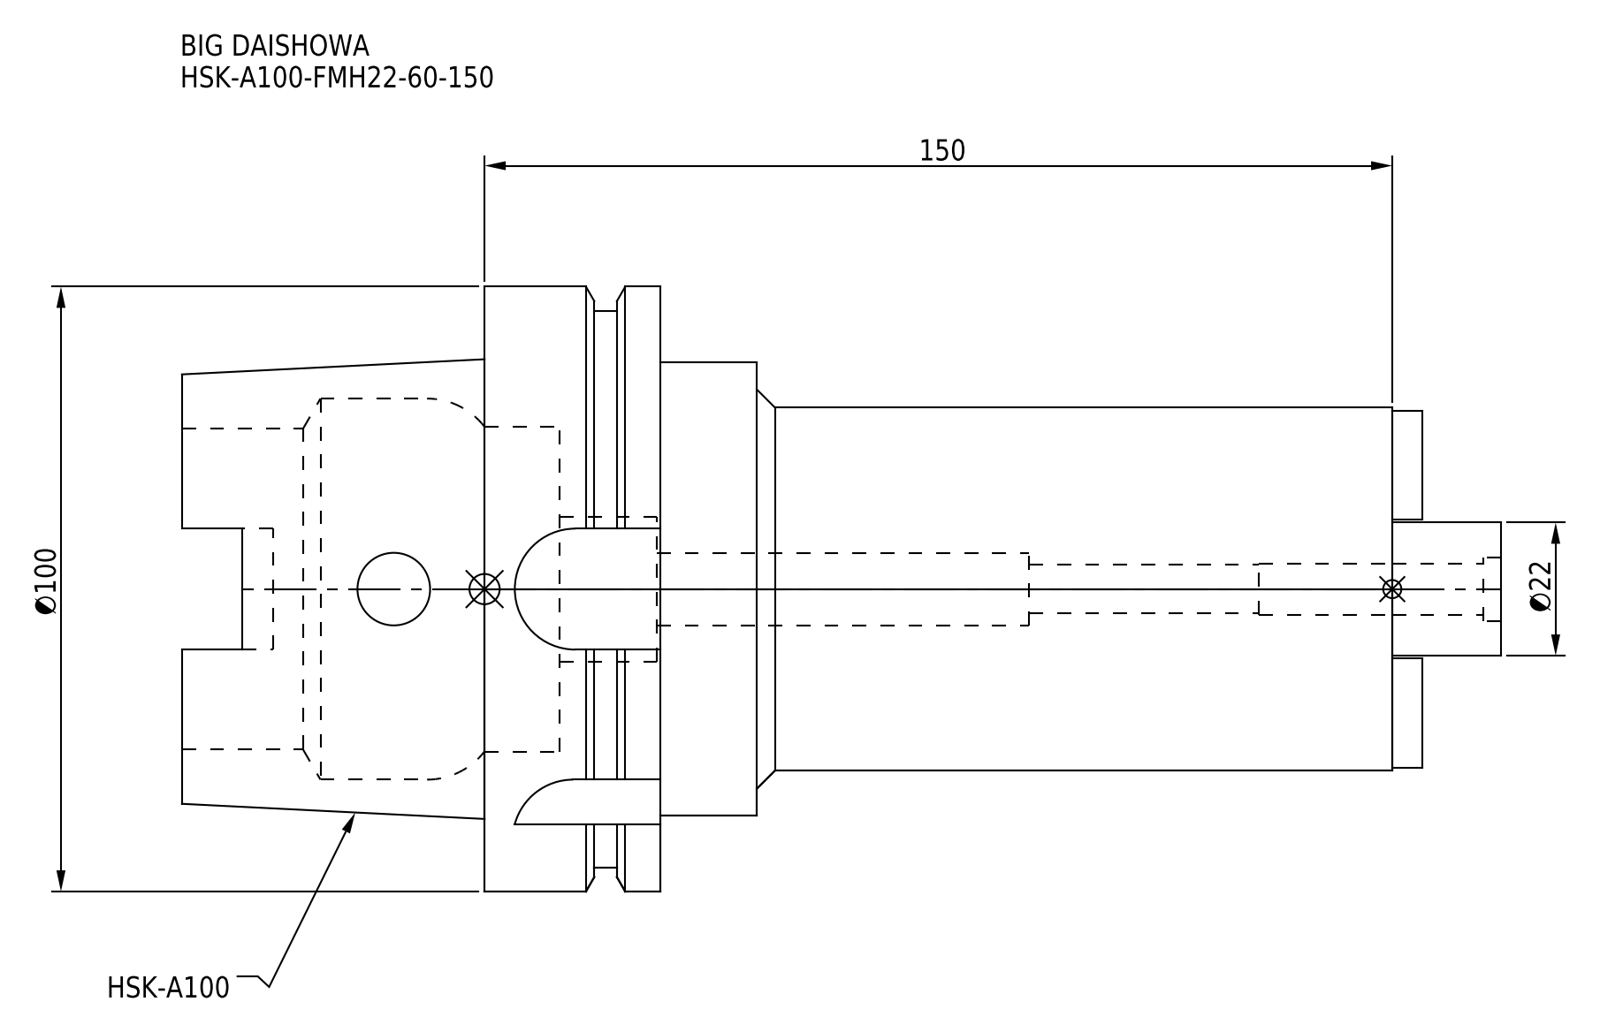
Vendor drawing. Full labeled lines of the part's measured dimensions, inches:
Part name (STEP PRODUCT): HSK-A100-FMH22-60-150
STEP written by: CREO PARAMETRIC BY PTC INC, 2016380 (AUTOMOTIVE_DESIGN)
Units: inches
Bodies: 1 solid, 109 faces (47 planar, 46 cylindrical, 16 other)
Overall size (bounding box): 8.583 × 3.937 × 3.937
Volume: 37.8 in³ · Surface area: 122.9 in²
Round holes (diameter × count): ⌀0.472 ×2, ⌀0.315 ×1, ⌀0.335 ×1, ⌀0.413 ×1, ⌀0.945 ×1, ⌀2.087 ×1, ⌀2.118 ×1, ⌀2.48 ×1
Round bosses / shafts (diameter × count): ⌀3.937 ×1, ⌀3.622 ×1, ⌀2.953 ×1, ⌀2.362 ×1, ⌀0.866 ×1
Partial cylindrical surfaces — rounded edges, fillets, slot ends (radius × count): R0.192 ×4, R0.394 ×4
Main face-to-face distances: 1.142, 0.652, 5.906, 4.764, 5.415, 0.49, 0.63, 1.772, 7.874, 3.11
